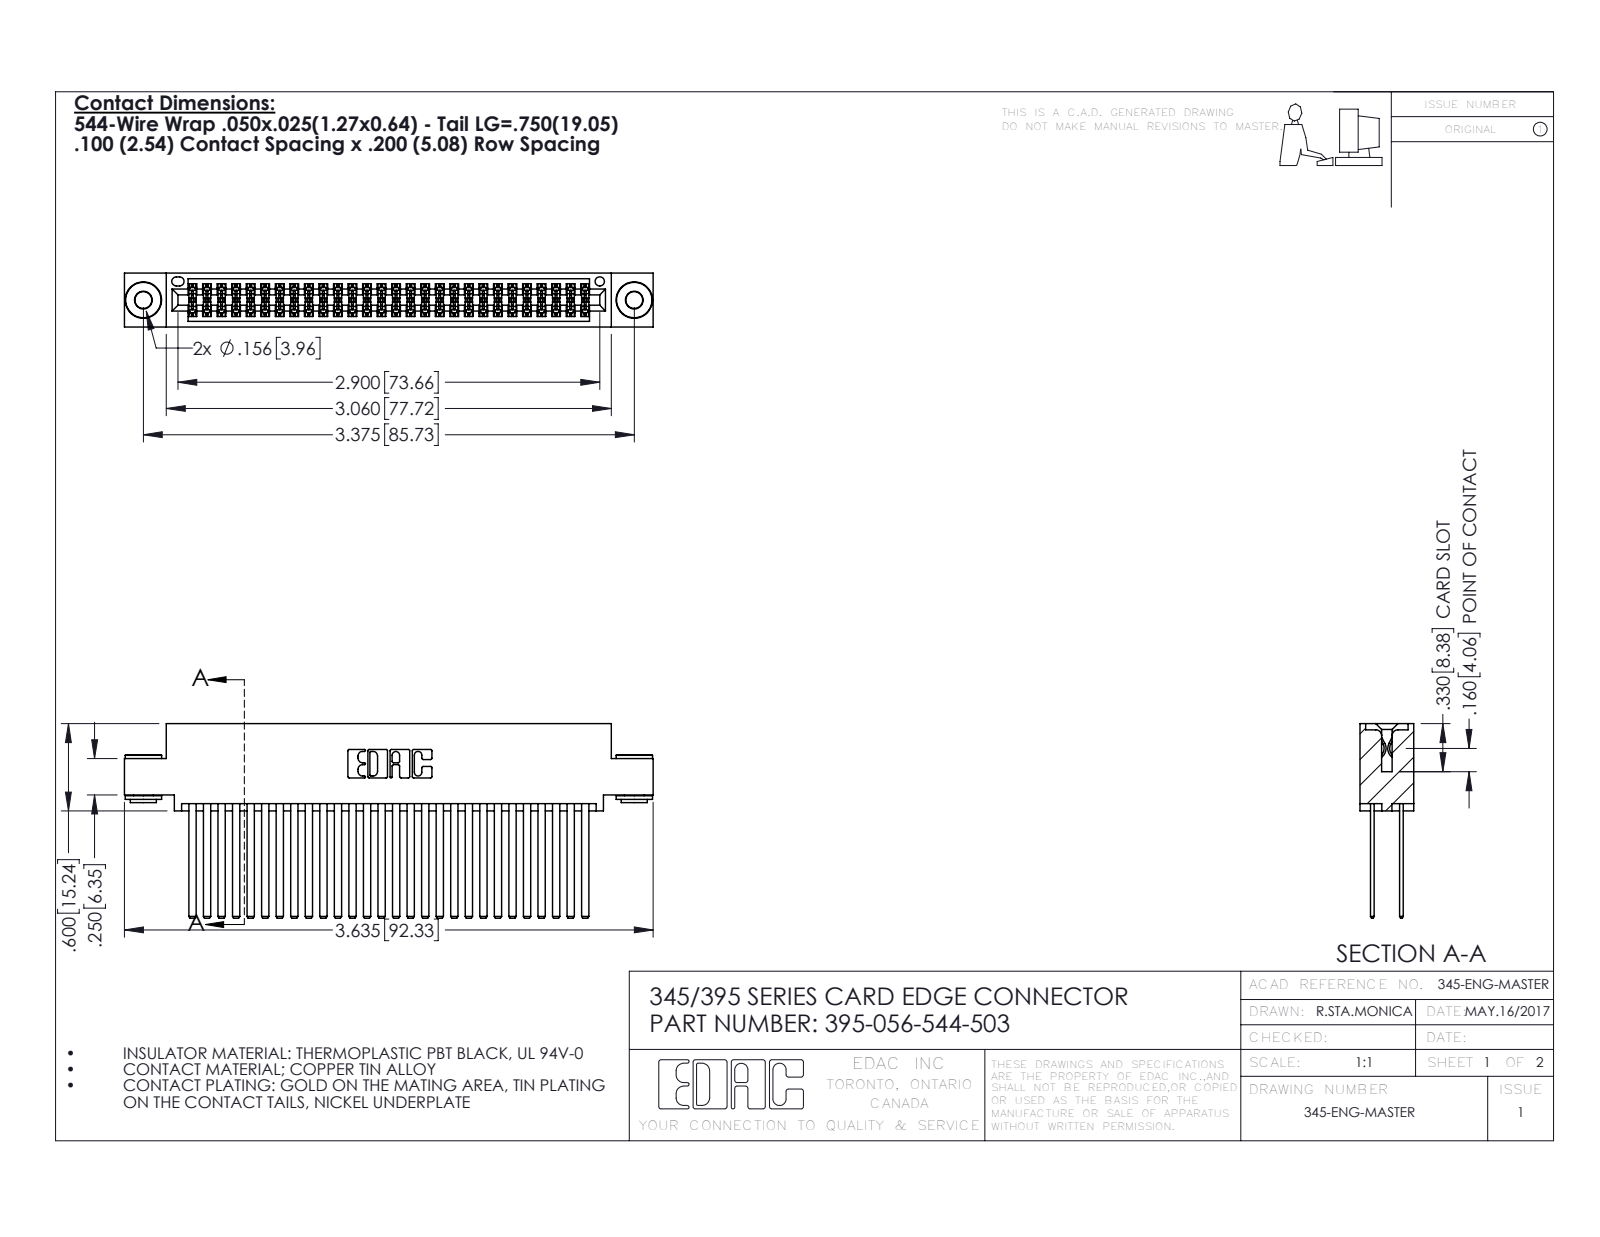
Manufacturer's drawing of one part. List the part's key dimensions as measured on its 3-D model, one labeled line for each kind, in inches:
Part name (STEP PRODUCT): 345-292-001_345-293-144; 345 Part_0.110 Offset - 0.156 Dia-TH; 395-056-544-503; 345-250-002_345-250-002-102
STEP written by: SolidWorks 2016 (CONFIG_CONTROL_DESIGN)
Units: inches
Bodies: 59 solids, 2632 faces (1718 planar, 906 cylindrical, 8 other)
Overall size (bounding box): 3.635 × 1.337 × 0.37
Volume: 0.584 in³ · Surface area: 25.53 in²
Round holes (diameter × count): ⌀0.116 ×2, ⌀0.156 ×2, ⌀0.064 ×1
Round bosses / shafts (diameter × count): ⌀0.25 ×2, ⌀0.18 ×2, ⌀0.136 ×2
Partial cylindrical surfaces — rounded edges, fillets, slot ends (radius × count): R0.006 ×84, R0.01 ×22, R0.007 ×6, R0.031 ×6, R0.026 ×3, R0.014 ×2, R0.019 ×2, R0.022 ×2
Main face-to-face distances: 0.2, 0.025, 0.072, 0.298, 0.272, 0.098, 0.225, 0.175, 0.37, 0.05
Hole centre spacings: 0.27, 3.14, 3.375
